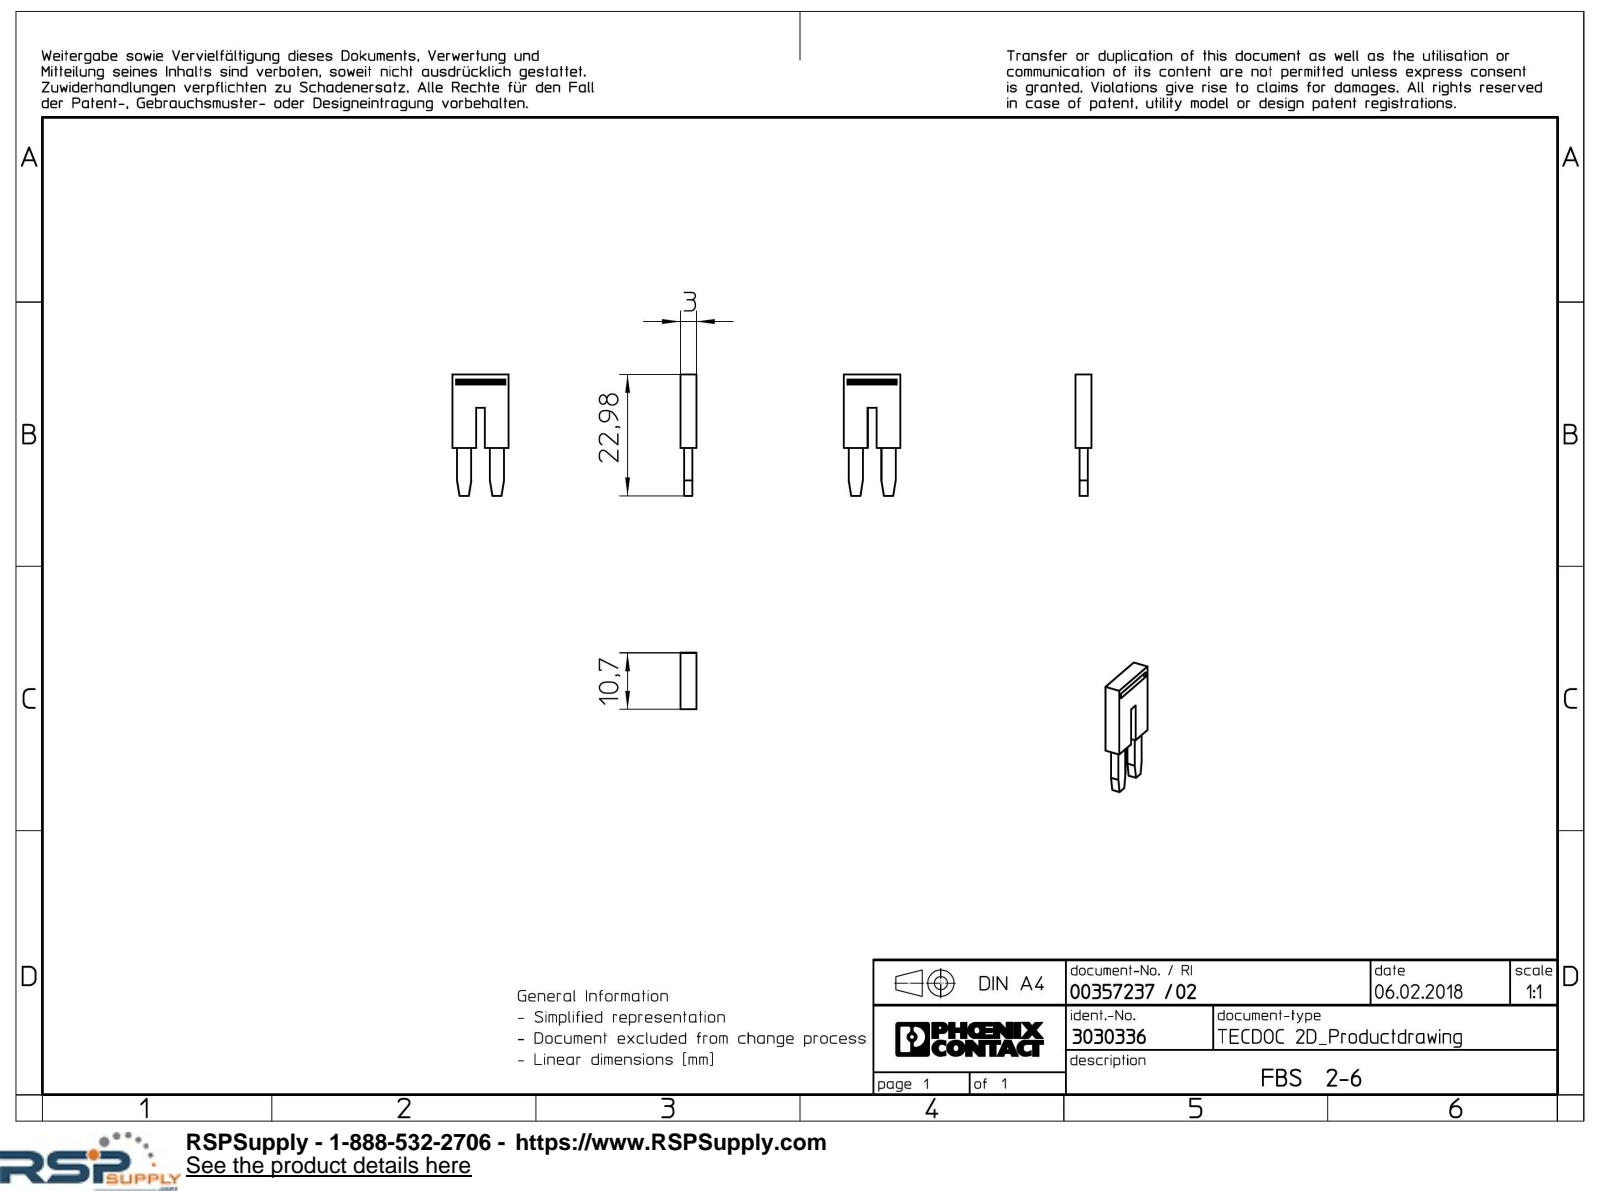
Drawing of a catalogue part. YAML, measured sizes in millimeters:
part_name: "FBS_2-6-select"
step_written_by: "Creo Elements/Direct Modeling 20.1A 29-Sep-2018 (C) Parametric Technology GmbH (AUTOMOTIVE_DESIGN)"
units: millimeters
bodies: {solids: 1, faces: 34, planar: 34, cylindrical: 0, other: 0}
overall_size: [22.98, 10.7, 3]
volume: 468
surface_area: 642
face_to_face_distances: [3, 0.7, 2.3, 6.2, 1.6, 4.5, 10.7, 0.91, 3.59, 1.7]
